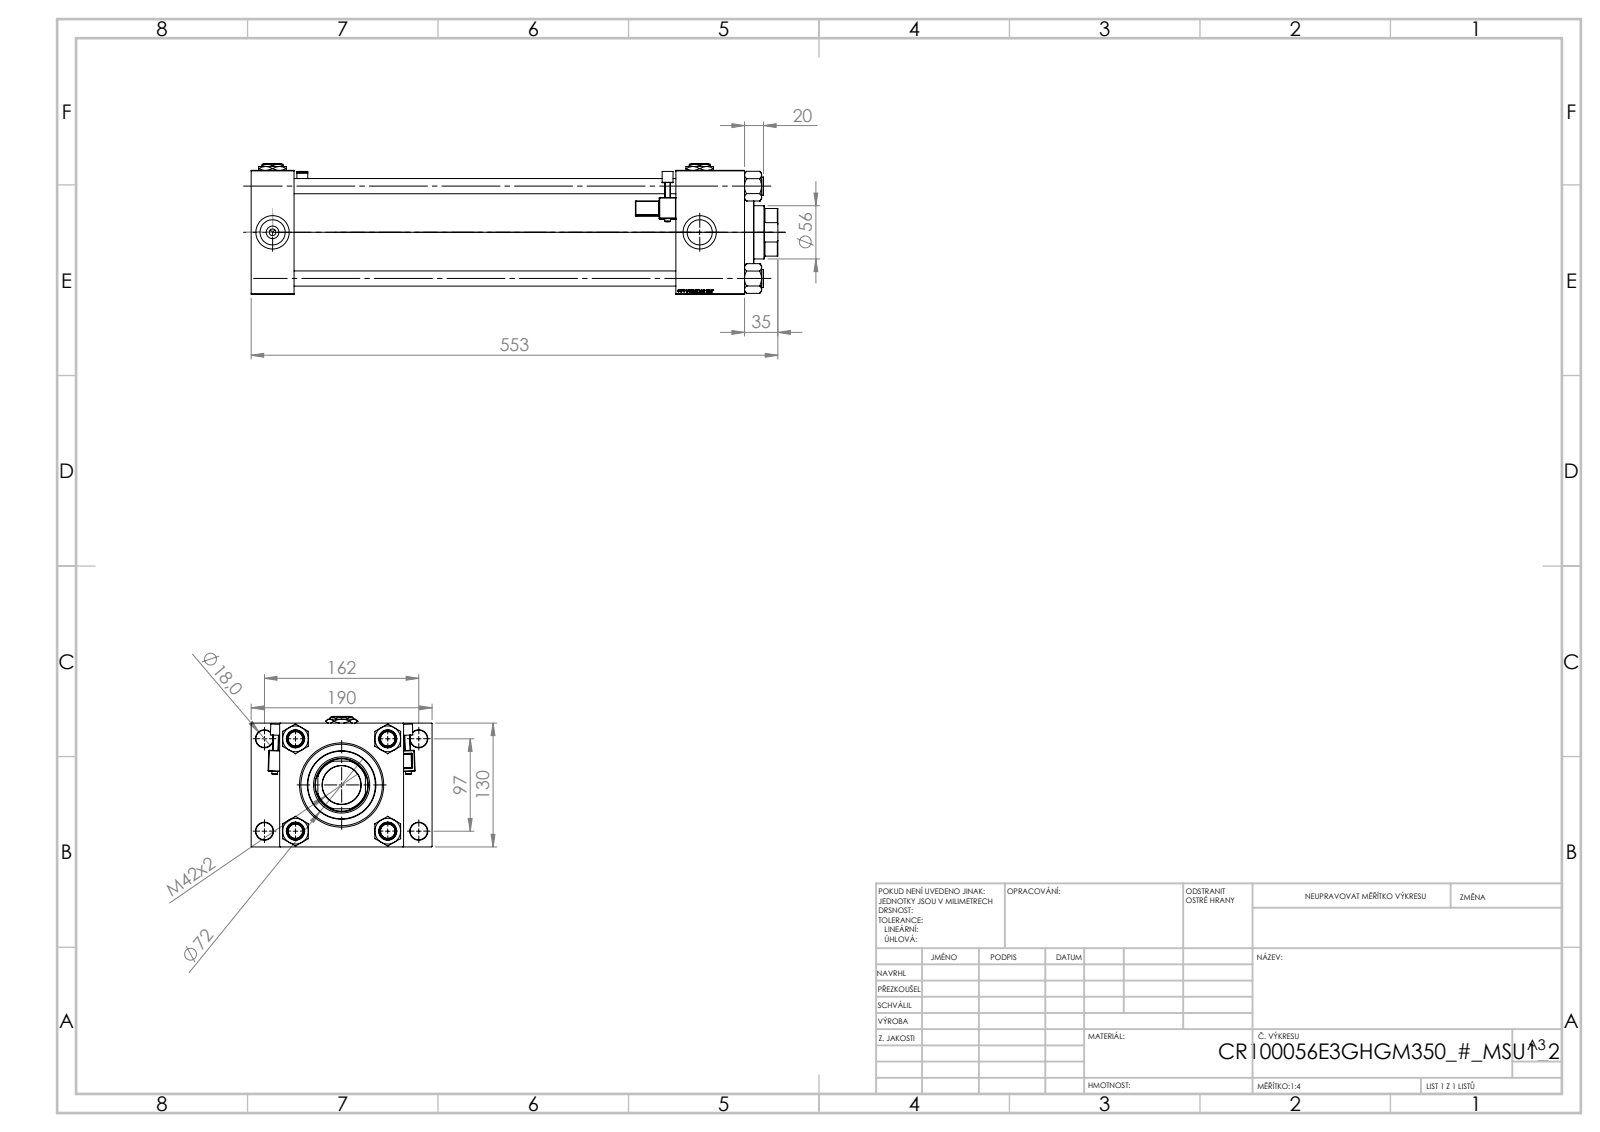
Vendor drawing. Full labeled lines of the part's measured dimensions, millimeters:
Part name (STEP PRODUCT): Zatka_pro_OIL_PORT; V215_VC_A; V215CR_VCP_E; V215CR_E_Body (+3 more)
STEP written by: SolidWorks 2019 (CONFIG_CONTROL_DESIGN)
Units: millimetres
Bodies: 15 solids, 1444 faces (653 planar, 161 cylindrical, 630 other)
Overall size (bounding box): 553 × 190 × 137
Volume: 4 220 000 mm³ · Surface area: 734 796 mm²
Round holes (diameter × count): ⌀16 ×4, ⌀18 ×4, ⌀26.44 ×4, ⌀35 ×4, ⌀7 ×3, ⌀2.5 ×2, ⌀40.5 ×1, ⌀56 ×1, ⌀59 ×1, ⌀76 ×1, ⌀85.5 ×1, ⌀100 ×1
Round bosses / shafts (diameter × count): ⌀19 ×4, ⌀6 ×2, ⌀106 ×1, ⌀72 ×1
Partial cylindrical surfaces — rounded edges, fillets, slot ends (radius × count): R0.5 ×48, R1 ×2, R2.5 ×2, R4 ×2, R27 ×1
Main face-to-face distances: 130, 45, 518, 473, 30, 446, 401, 72, 160, 96
Hole centre spacings: 32.55, 49.02, 62.87, 68.52, 94.41, 96.9, 101.73, 102.27
